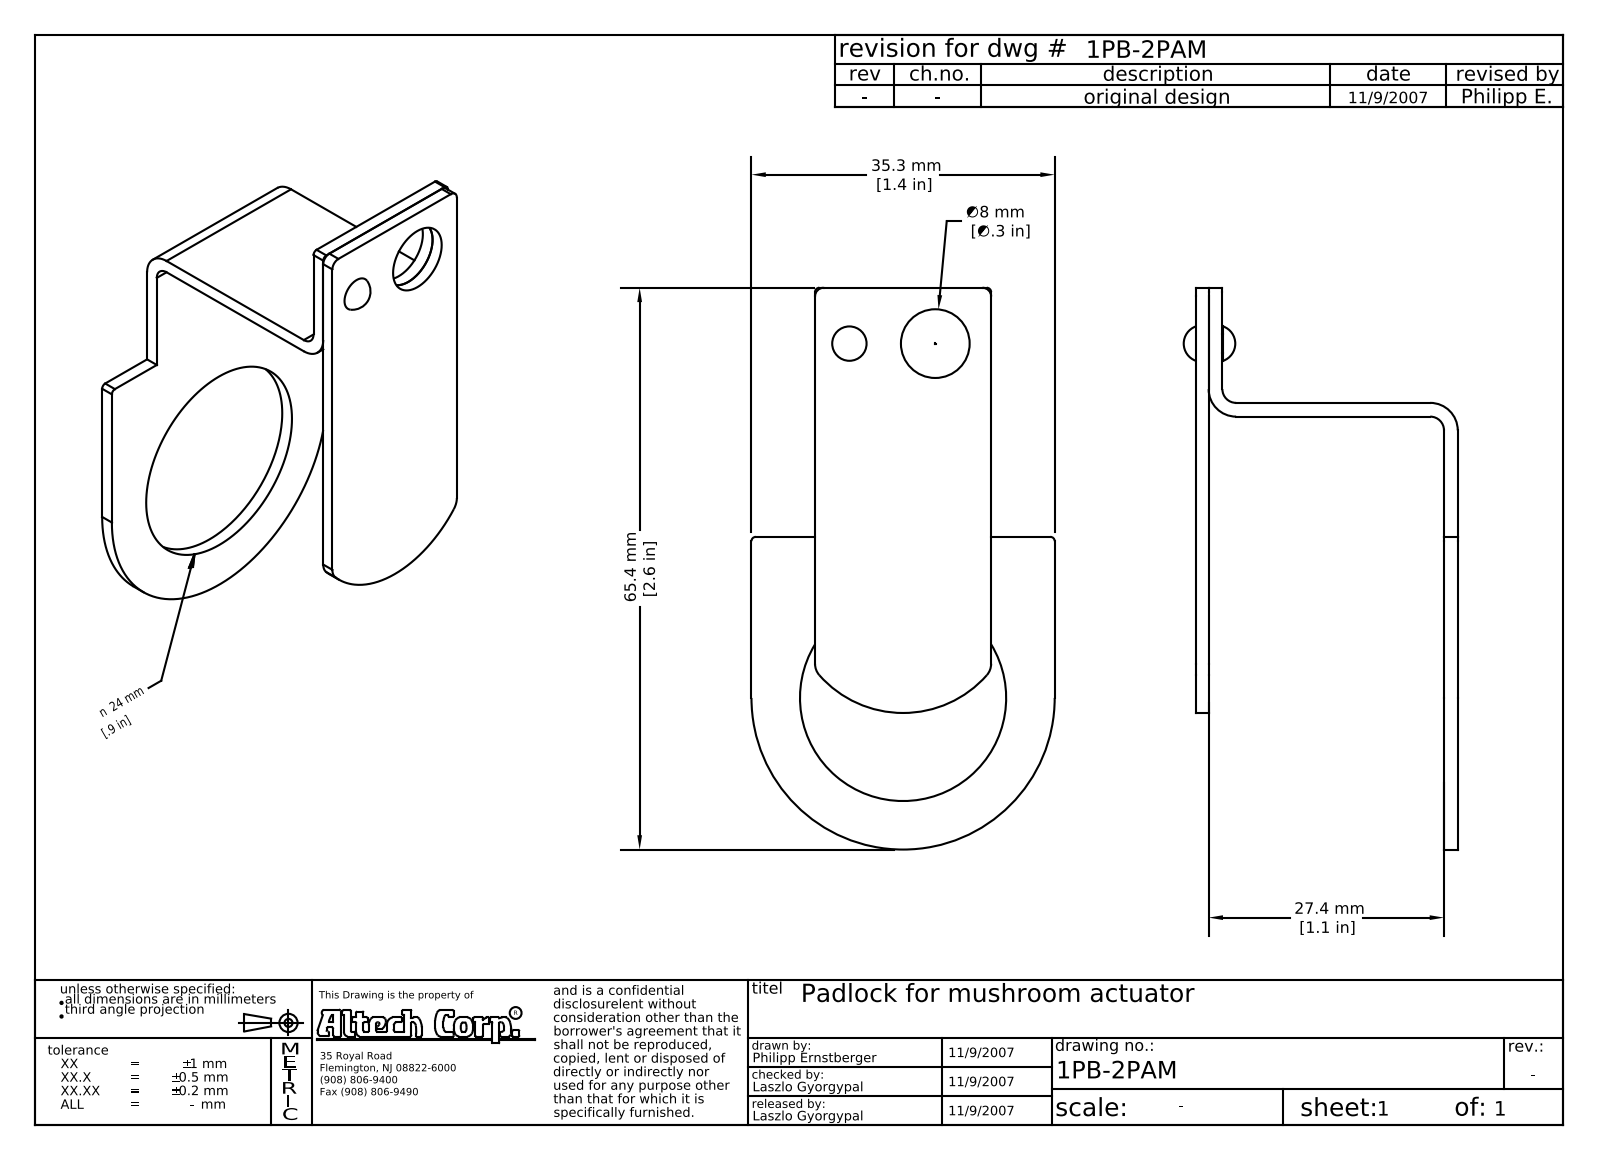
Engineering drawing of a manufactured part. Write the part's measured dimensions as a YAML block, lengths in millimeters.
part_name: "2PAM; standoff; top; SS 1440 - KN 2.3 x 18 x 3"
step_written_by: "Autodesk Inventor 2008 (AUTOMOTIVE_DESIGN)"
units: millimeters
bodies: {solids: 3, faces: 42, planar: 20, cylindrical: 20, other: 2}
overall_size: [65.4, 35.3, 31.9]
volume: 4238
surface_area: 6247
round_holes:
  - {diameter: 2.5, count: 1}
  - {diameter: 8, count: 1}
  - {diameter: 24, count: 1}
round_bosses_or_shafts:
  - {diameter: 2.3, count: 1}
partial_cylinders:
  - {radius: 0.5, count: 4}
  - {radius: 1, count: 2}
  - {radius: 1.6, count: 2}
  - {radius: 2, count: 2}
  - {radius: 3.2, count: 2}
  - {radius: 13, count: 1}
  - {radius: 17.65, count: 1}
face_to_face_distances: [1.6, 27.4, 29, 30.5, 28.9, 1.5, 25.8, 3.1, 20.5, 15]
hole_center_spacings: [10, 41.42, 41.72]
